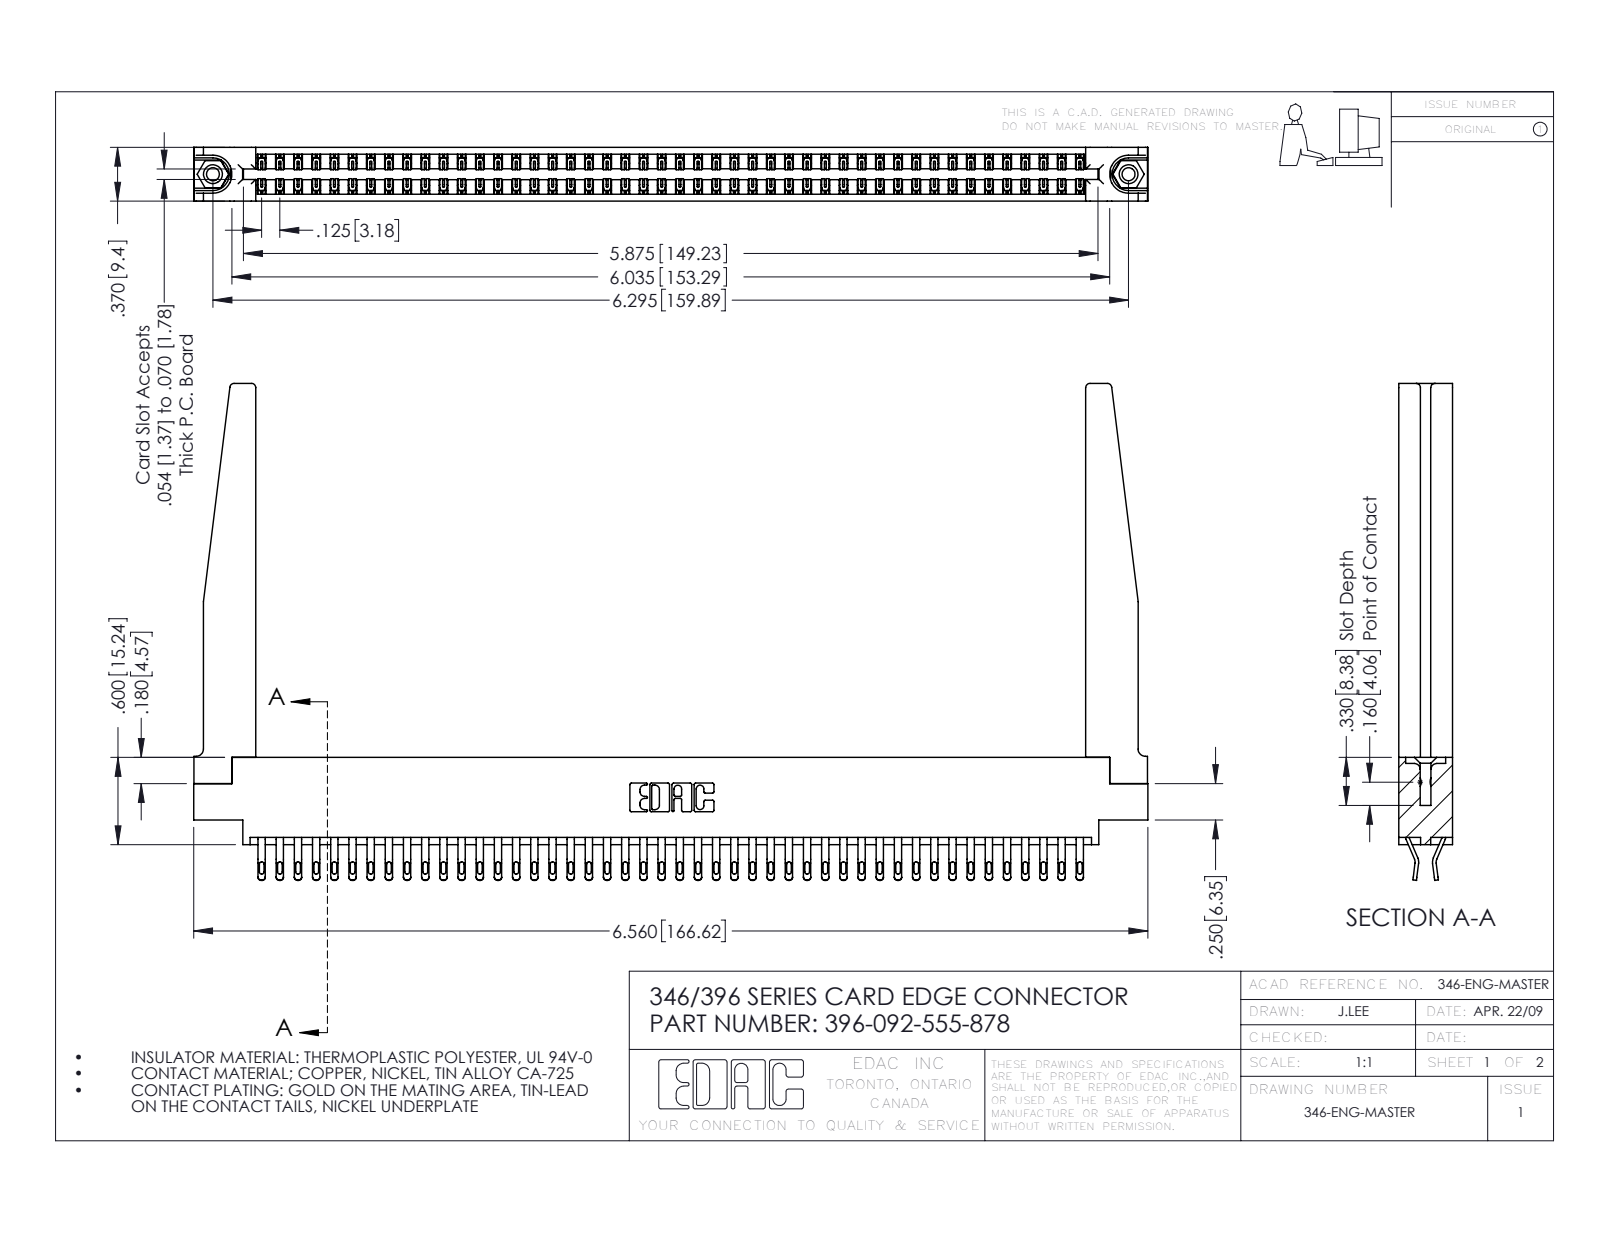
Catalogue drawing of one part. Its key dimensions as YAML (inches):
part_name: "346 Part_0.170 Offset - 0.156 Dia-TH; 345-250-001_345-250-001-102; 345-292-001_555 Tail; 396-092-555-878 (+1 more)"
step_written_by: "SolidWorks 2016 (CONFIG_CONTROL_DESIGN)"
units: inches
bodies: {solids: 97, faces: 5696, planar: 3258, cylindrical: 2386, other: 52}
overall_size: [6.56, 3.415, 0.37]
volume: 1.422
surface_area: 46.91
round_holes:
  - {diameter: 0.089, count: 2}
  - {diameter: 0.125, count: 2}
  - {diameter: 0.156, count: 2}
  - {diameter: 0.064, count: 1}
round_bosses_or_shafts:
  - {diameter: 0.155, count: 2}
partial_cylinders:
  - {radius: 0.016, count: 184}
  - {radius: 0.02, count: 184}
  - {radius: 0.006, count: 138}
  - {radius: 0.01, count: 22}
  - {radius: 0.03, count: 8}
  - {radius: 0.007, count: 6}
  - {radius: 0.031, count: 6}
  - {radius: 0.05, count: 4}
face_to_face_distances: [0.37, 0.048, 0.322, 0.072, 0.15, 0.148, 0.25, 0.025, 0.298, 0.275]
hole_center_spacings: [0.246, 6.086, 6.295]
